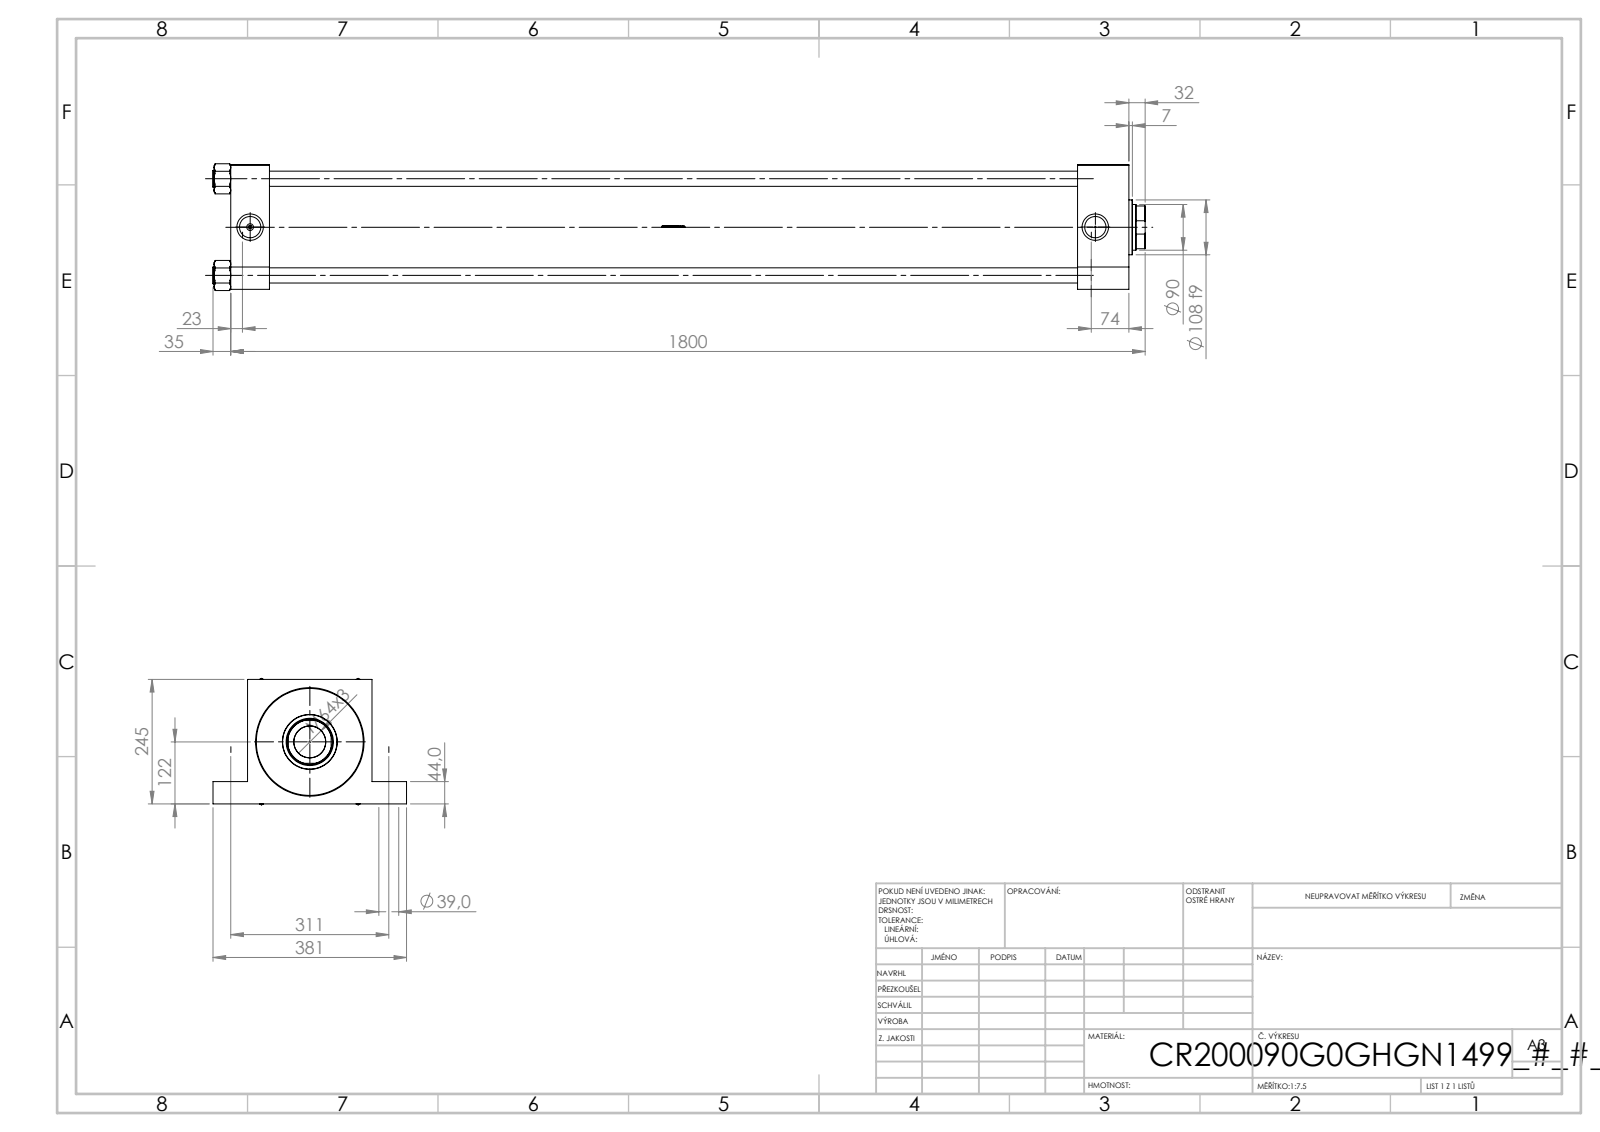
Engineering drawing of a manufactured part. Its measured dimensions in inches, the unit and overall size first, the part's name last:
Units: inches
Overall size (bounding box): 72.244 × 15 × 9.82
Round holes (diameter × count): ⌀1.181 ×4, ⌀1.535 ×4, ⌀0.276 ×2, ⌀1.65 ×2, ⌀2.047 ×2, ⌀2.461 ×1, ⌀3.543 ×1, ⌀3.661 ×1, ⌀5.748 ×1, ⌀7.874 ×1, ⌀8.287 ×1
Round bosses / shafts (diameter × count): ⌀1.299 ×4, ⌀8.11 ×1, ⌀4.252 ×1
Partial cylindrical surfaces — rounded edges, fillets, slot ends (radius × count): R1.732 ×1
Main face-to-face distances: 9.646, 2.992, 69.606, 66.614, 68.476, 65.484, 1.13, 3.976, 65.63, 62.638
Hole centre spacings: 7.488, 5.281, 5.309, 10.59, 12.244, 65.787, 66.917, 65.512
Volume: 1 881 in³ · Surface area: 6 154 in²
Bodies: 11 solids, 1135 faces (479 planar, 124 cylindrical, 532 other)
Part name (STEP PRODUCT): V215CR_G_Body; NUT_M5_G; V215CR_VCP_G; V215_VC_A (+1 more)
STEP written by: SolidWorks 2019 (CONFIG_CONTROL_DESIGN)
